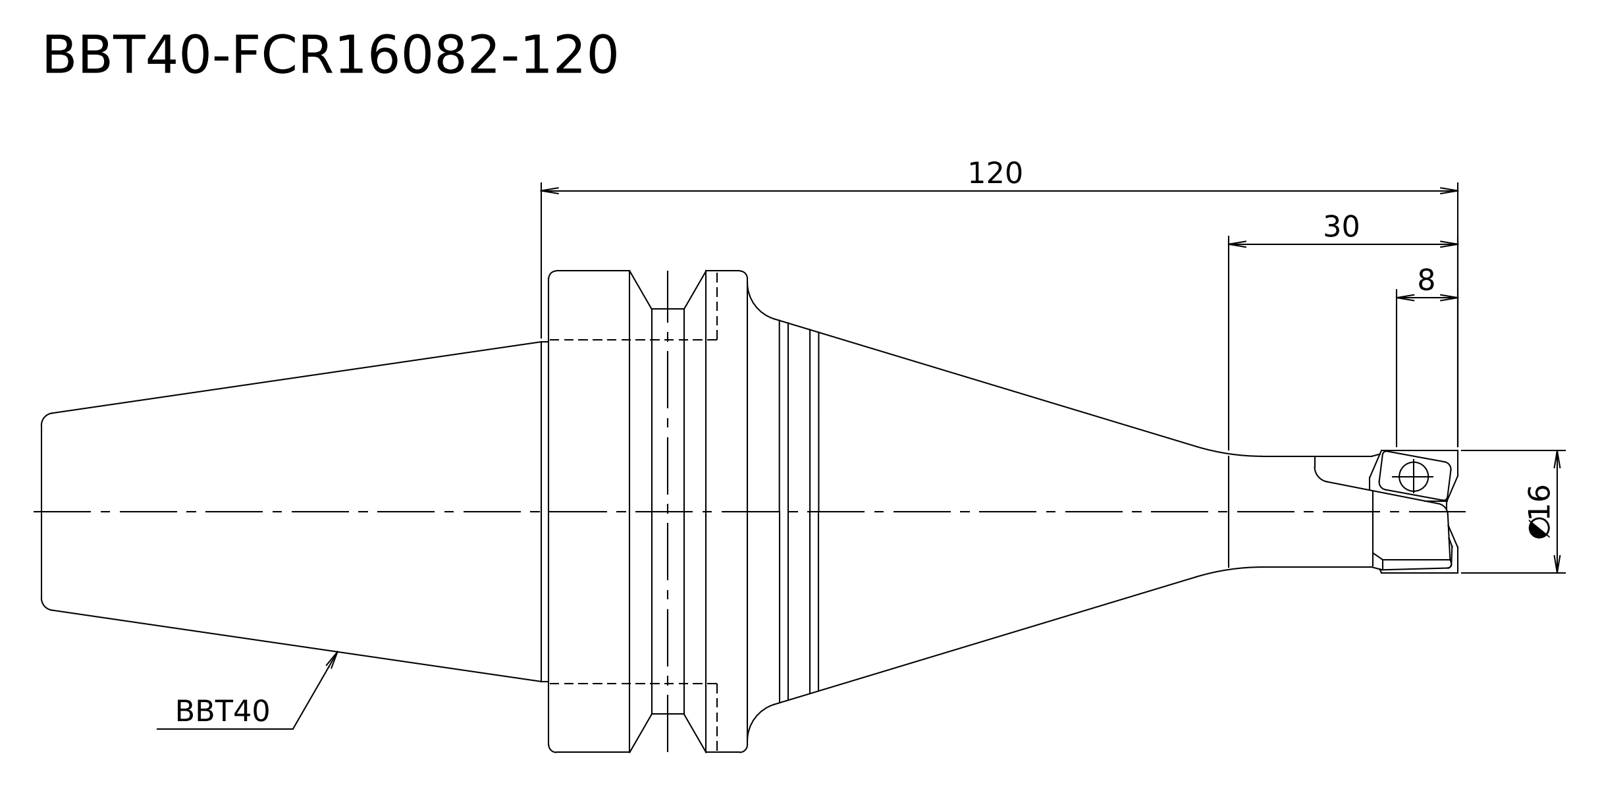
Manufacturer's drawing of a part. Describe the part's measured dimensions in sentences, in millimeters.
Its 3-D file was written by "Kubotek KeyCreator V8.5.1 (14335) (CONFIG_CONTROL_DESIGN)". It is 1 solid with 17 faces: 4 planar, 6 cylindrical and 7 other. Overall it measures 185.4 by 63 by 63 millimeters. Its volume is 208 400 cubic millimeters and its surface area 24 722 square millimeters. Round bosses or shafts: 1 of diameter 63, 1 of diameter 53, 1 of diameter 44.45, 1 of diameter 16, 1 of diameter 14.5. The main face-to-face distances are 66.4, 26, 92.4, 93, 119, 185.4.
